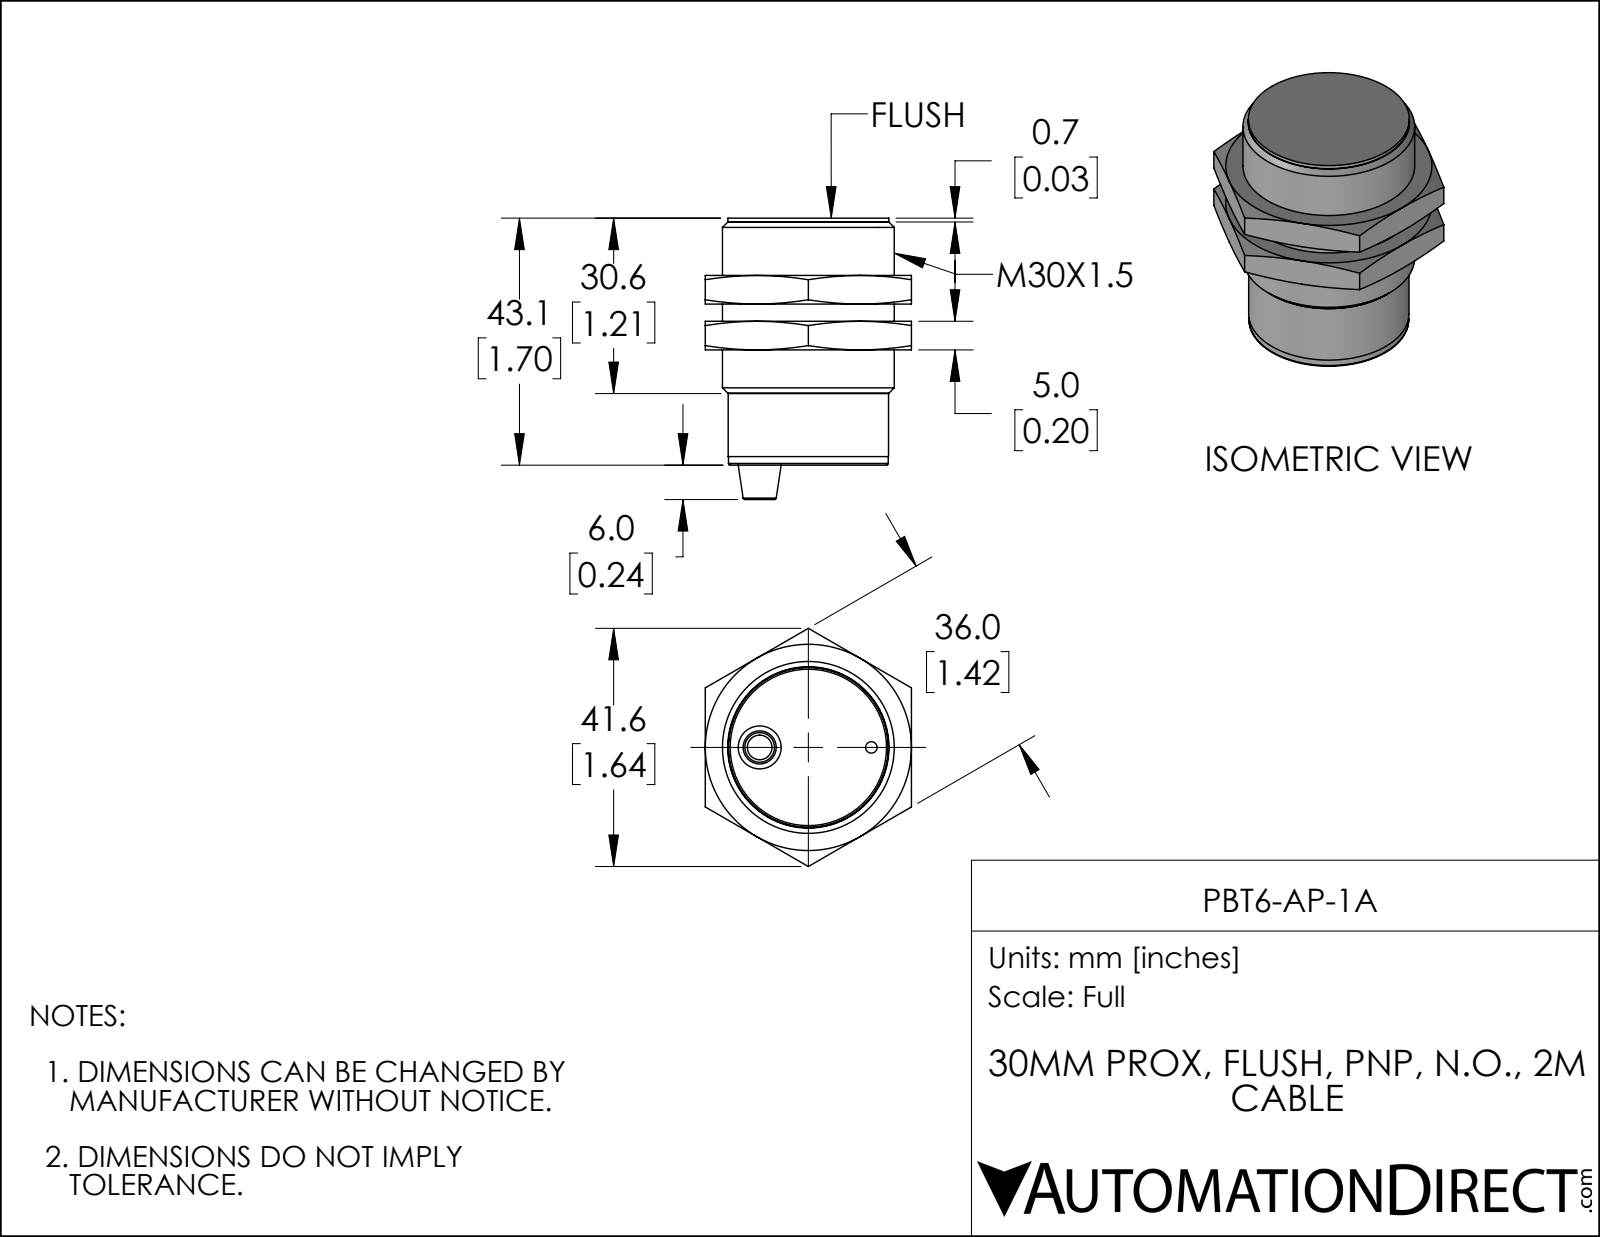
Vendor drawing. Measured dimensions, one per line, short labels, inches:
name: DSD-0298
written by: SolidWorks 2019 (AUTOMOTIVE_DESIGN)
unit: in
bodies: 1 solid, 19 faces (6 planar, 6 cylindrical, 7 other)
size: 1.934 × 1.181 × 1.181
volume: 1.787 in³; area: 8.492 in²
holes: 1× ⌀0.079, 1× ⌀0.169
bosses: 1× ⌀1.181, 1× ⌀1.106, 1× ⌀1.102, 1× ⌀1.098
face distances: 1.698, 1.658, 0.039, 1.934, 0.276, 0.236, 1.639, 0.02, 0.059, 0.295
hole spacings: 0.768
